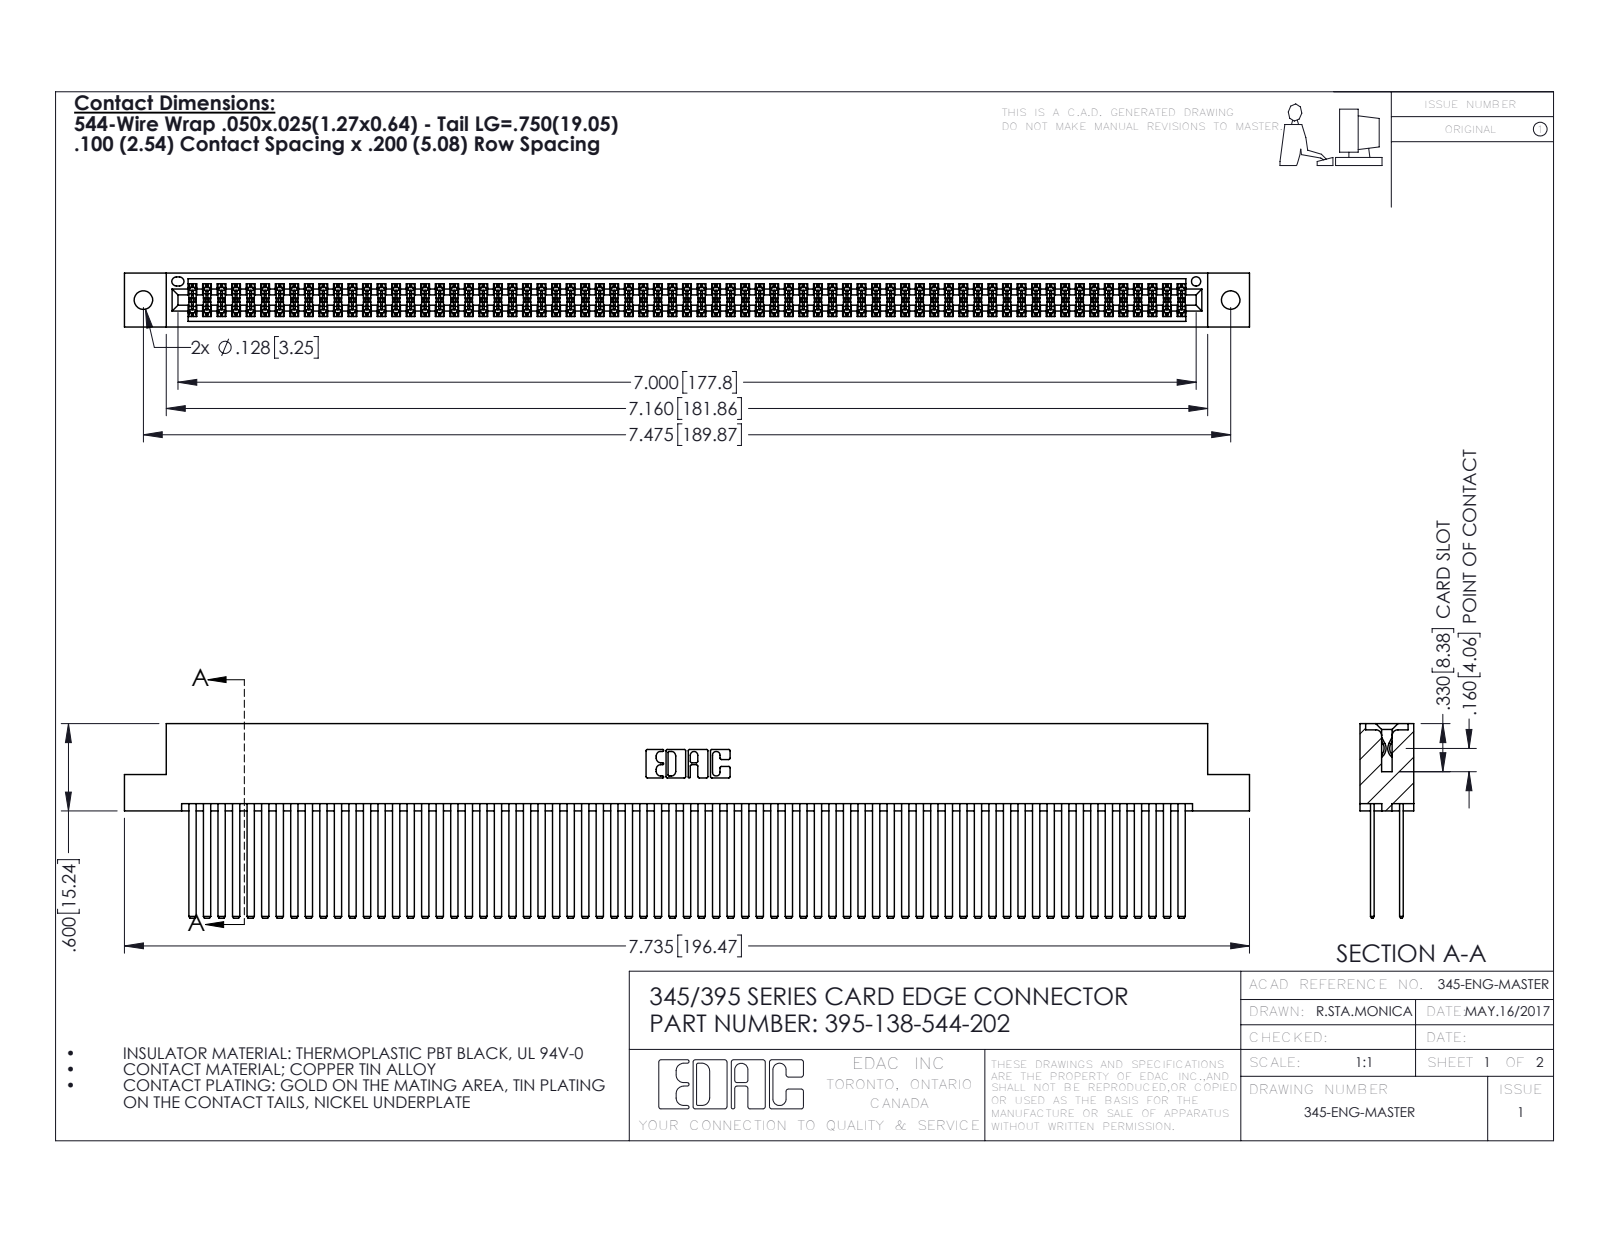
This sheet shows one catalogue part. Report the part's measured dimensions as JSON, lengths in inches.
{"part_name": "345-292-001_345-293-144; 395-138-544-202; 345 Part_Flush Mounting Lugs - 0.128 Dia", "step_written_by": "SolidWorks 2016 (CONFIG_CONTROL_DESIGN)", "units": "inches", "bodies": {"solids": 139, "faces": 6198, "planar": 4082, "cylindrical": 2116, "other": 0}, "overall_size": [7.735, 1.337, 0.37], "volume_in3": 1.296, "surface_area_in2": 57.83, "round_holes": [[0.128, 2], [0.064, 1]], "partial_cylinders_radius": [[0.006, 207], [0.01, 22], [0.007, 6], [0.031, 6], [0.026, 3], [0.014, 2], [0.019, 2], [0.022, 2]], "face_to_face_distances": [0.2, 0.025, 0.298, 0.072, 0.098, 0.272, 0.225, 0.175, 0.37, 0.05], "hole_center_spacings": [0.27, 7.239, 7.475]}
